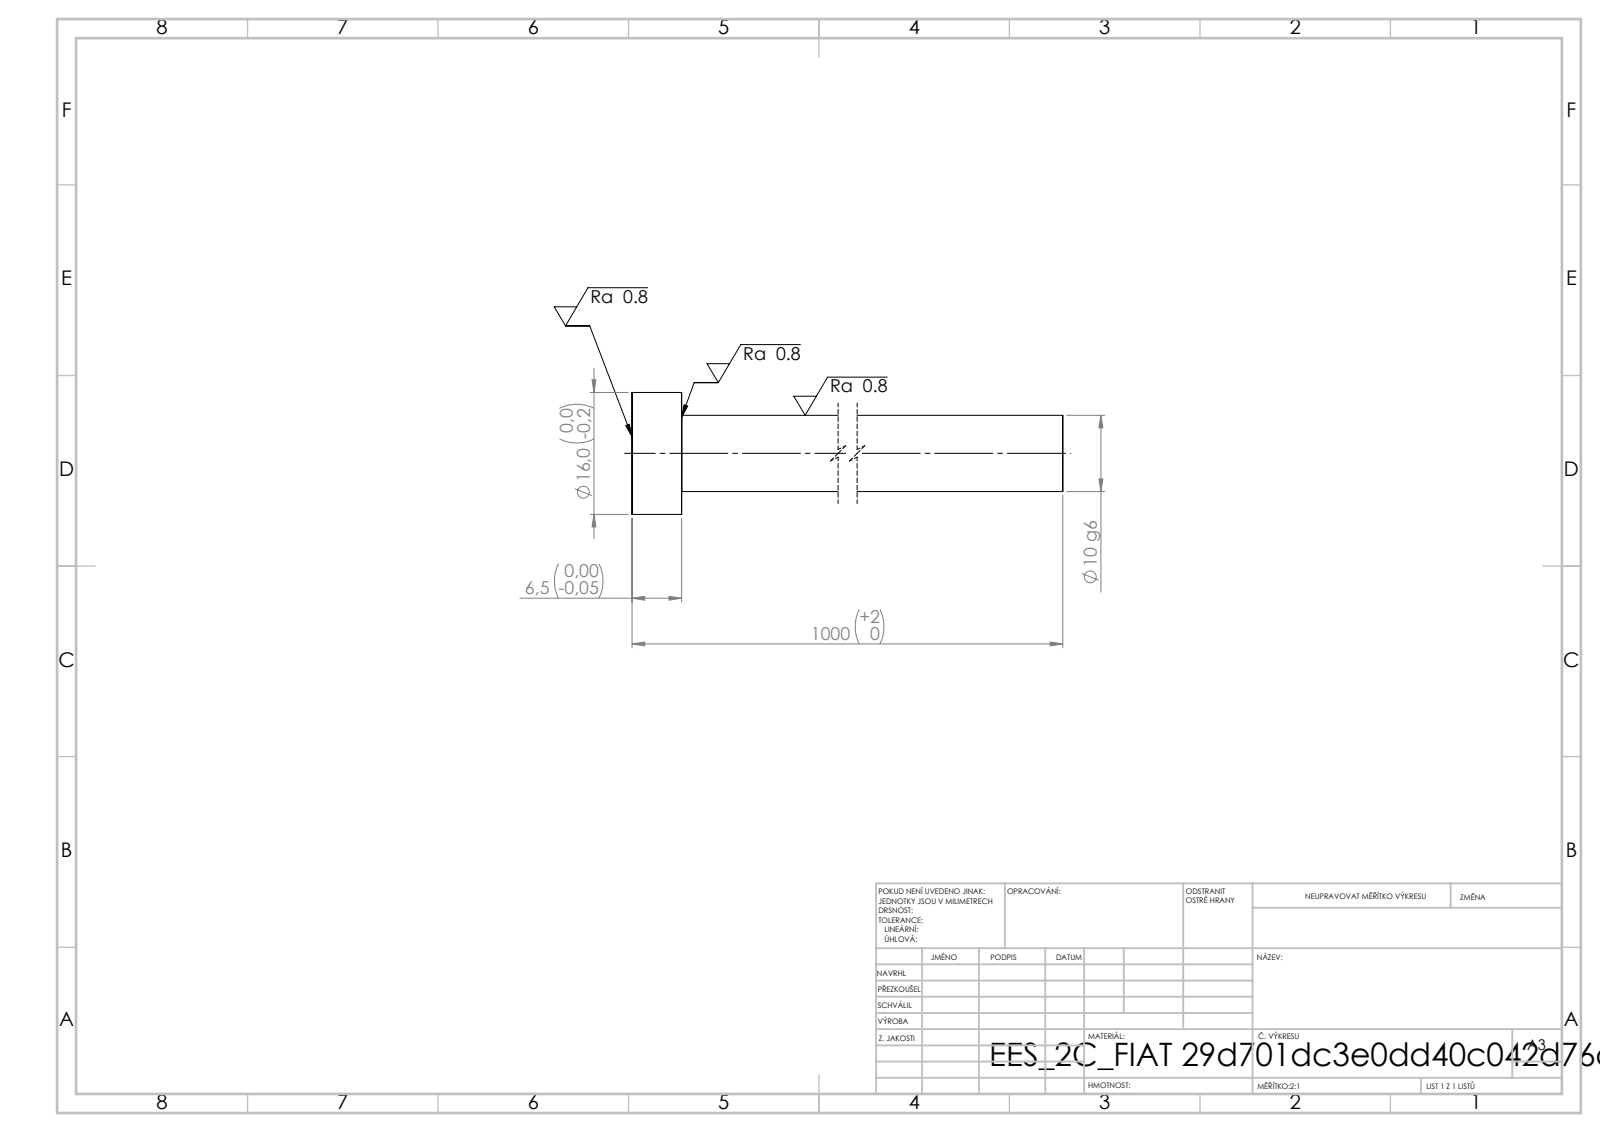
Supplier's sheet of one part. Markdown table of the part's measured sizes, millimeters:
| quantity | value |
| --- | --- |
| STEP written by | SolidWorks 2019 (CONFIG_CONTROL_DESIGN) |
| units | millimeters |
| bodies | 1 solid, 7 faces (3 planar, 4 cylindrical, 0 other) |
| overall size | 1000 × 16 × 16 |
| volume | 79 336 mm³ |
| surface area | 31 941 mm² |
| round bosses / shafts (diameter × count) | 16 × 1, 10 × 1 |
| main face-to-face distances | 6.5, 1000, 993.5 |
